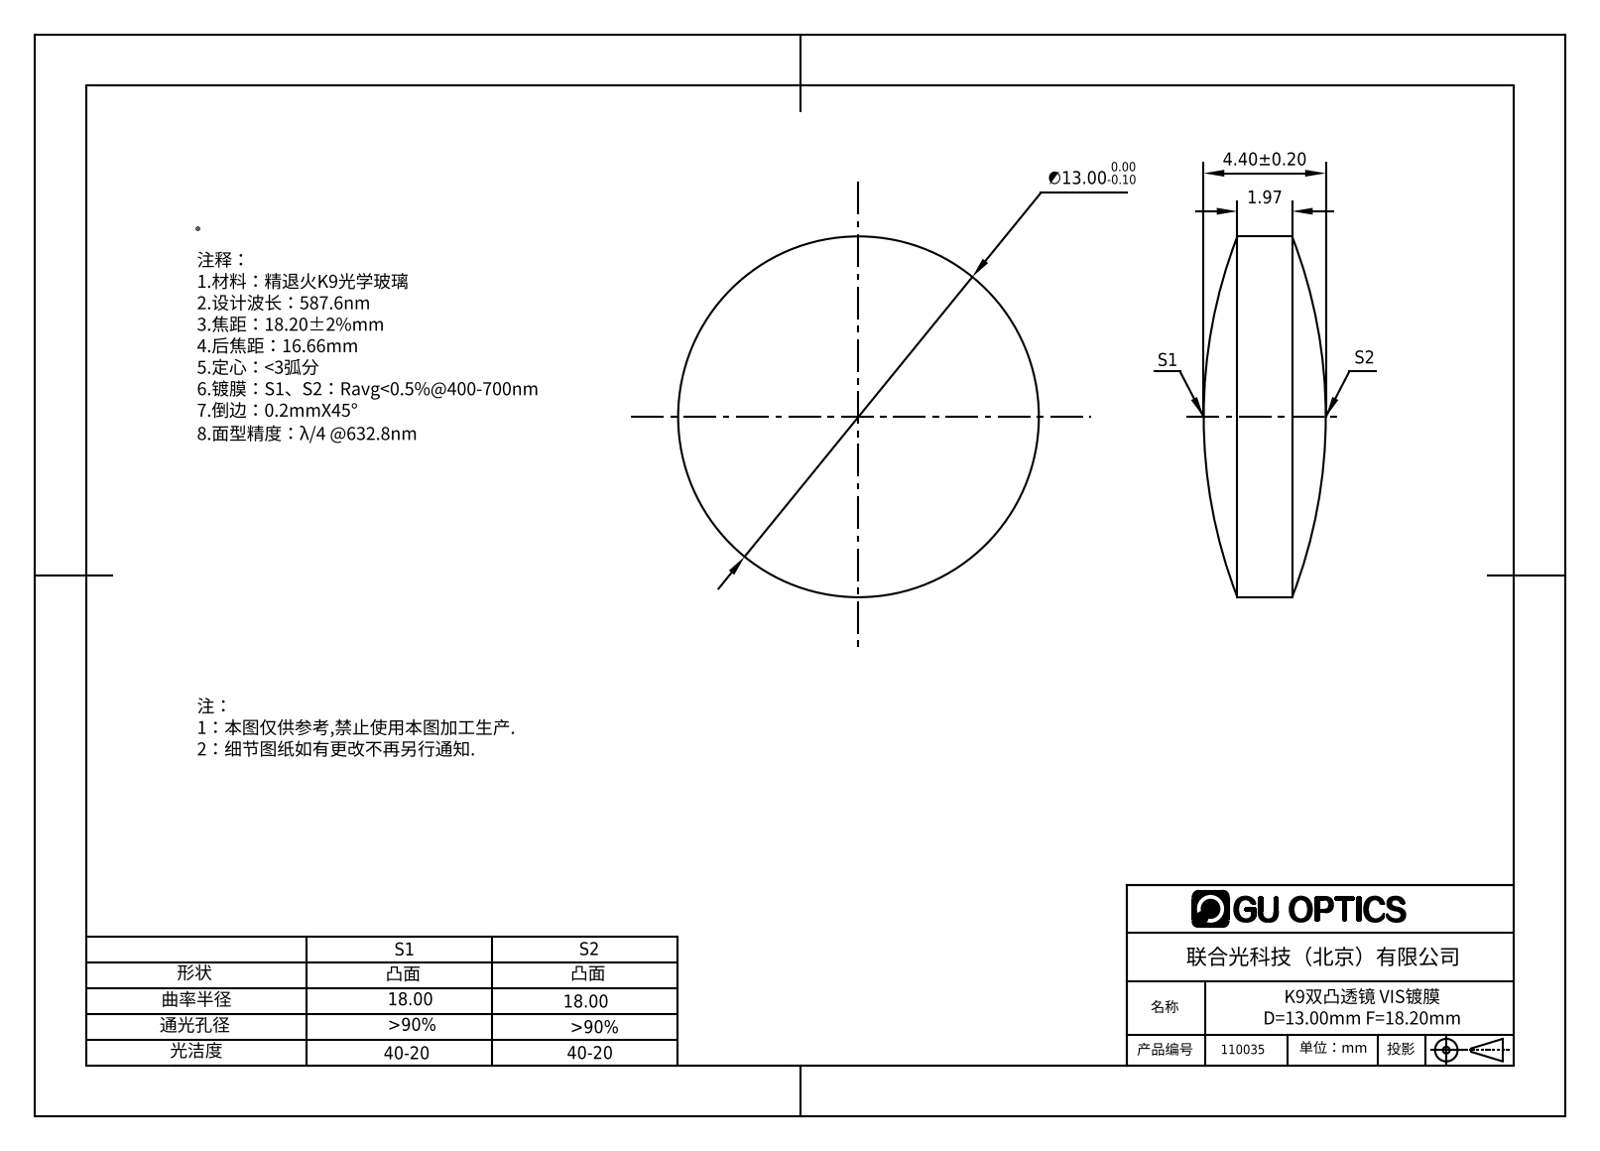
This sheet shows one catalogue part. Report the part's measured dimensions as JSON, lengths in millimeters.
{"part_name": "110013", "step_written_by": "SolidWorks 2016 (CONFIG_CONTROL_DESIGN)", "units": "millimeters", "bodies": {"solids": 1, "faces": 6, "planar": 0, "cylindrical": 2, "other": 4}, "overall_size": [13, 13, 4.4], "volume_mm3": 425, "surface_area_mm2": 355, "round_bosses_or_shafts": [[13, 1]]}
